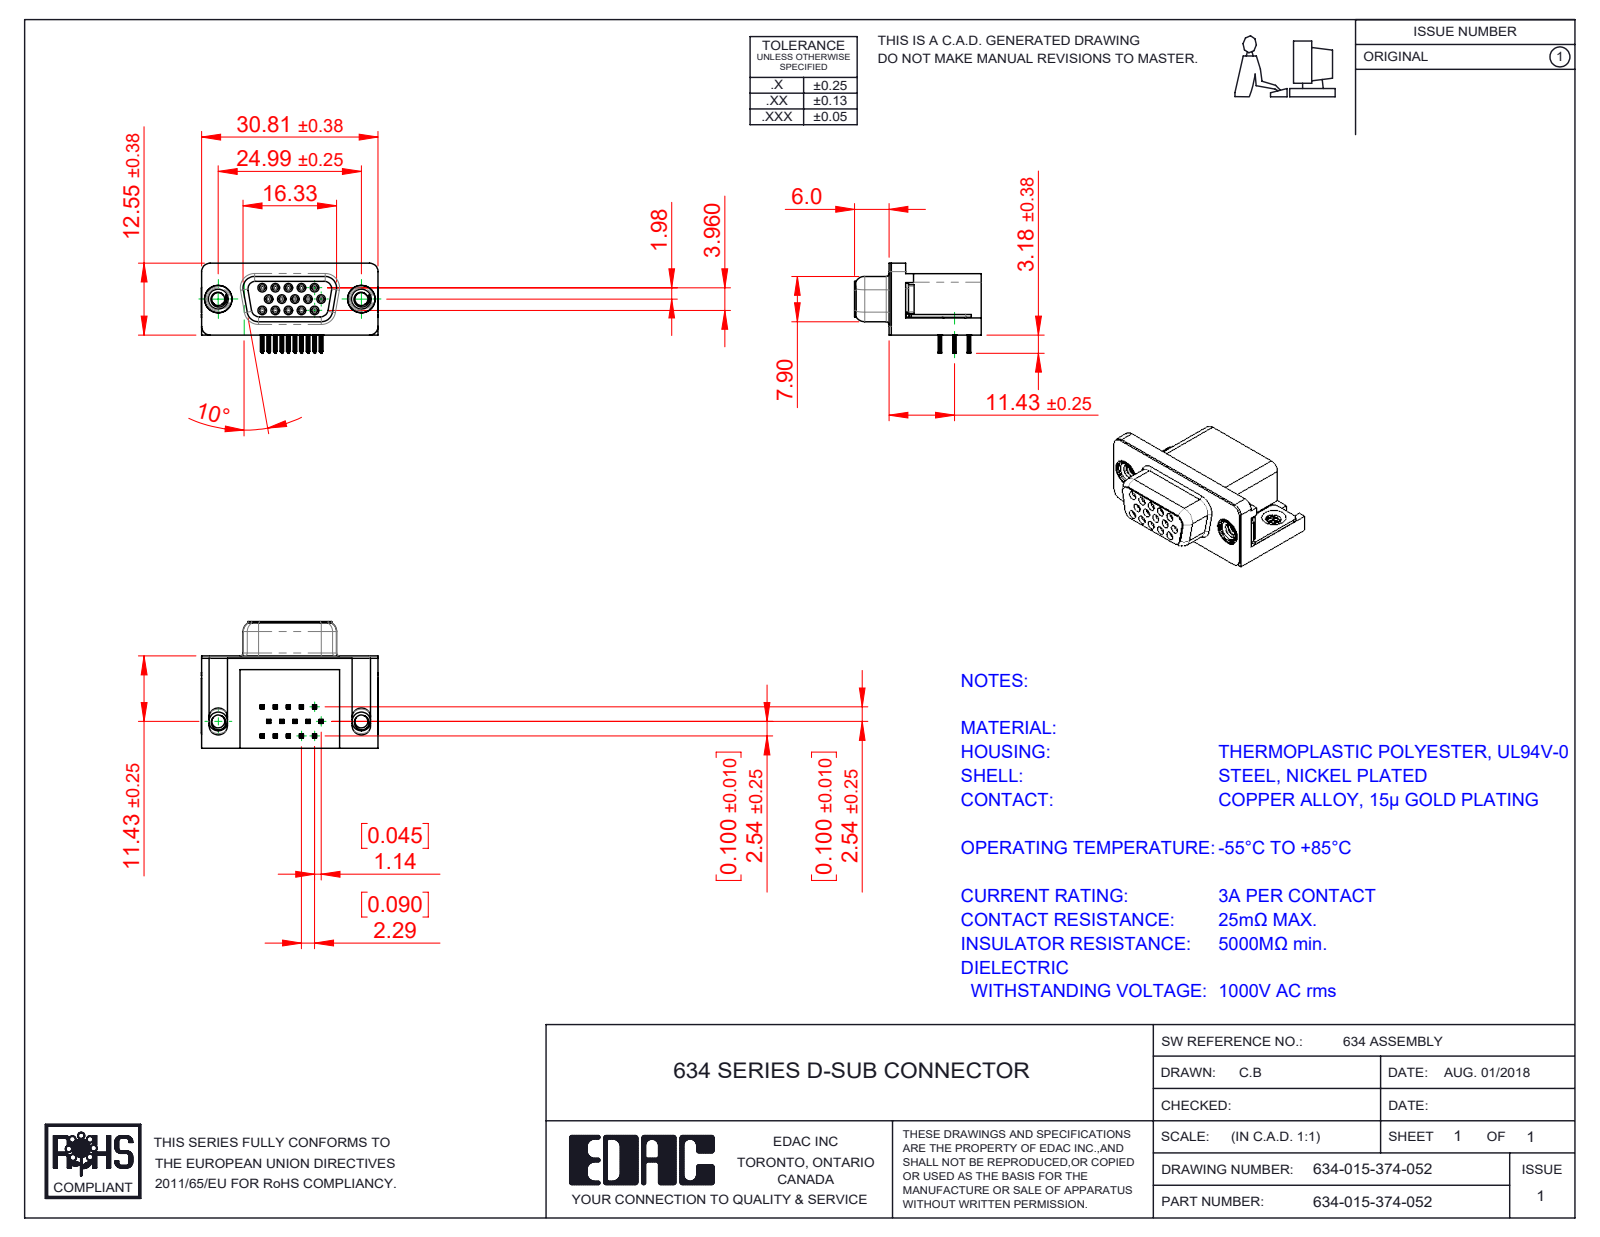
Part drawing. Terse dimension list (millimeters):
name: Contact Middle_Recessed; 4-40 Threaded Rivet; Contact Bottom; 634 Shell (+5 more)
written by: SolidWorks 2016 (CONFIG_CONTROL_DESIGN)
unit: mm
bodies: 21 solids, 2451 faces (1066 planar, 611 cylindrical, 774 other)
size: 30.89 × 22.1 × 15.73
volume: 4 566 mm³; area: 6 578 mm²
holes: 15× ⌀0.8, 15× ⌀0.9, 4× ⌀2.26, 2× ⌀4, 2× ⌀4.8, 2× ⌀5
bosses: 15× ⌀1.2, 2× ⌀4.9, 2× ⌀4.75, 2× ⌀3.9, 2× ⌀3.26
rounds: 120× R0.1, 60× R0.15, 30× R0.35, 19× R1, 15× R0.34, 8× R0.25, 8× R1.35, 8× R1.6
face distances: 0.4, 10.35, 15.7, 16.1, 0.35, 2.5, 0.6, 2.9, 6.4, 0.5
hole spacings: 2.29, 2.28, 3.96, 4.57, 6.05, 3.97, 4.58, 6.86
